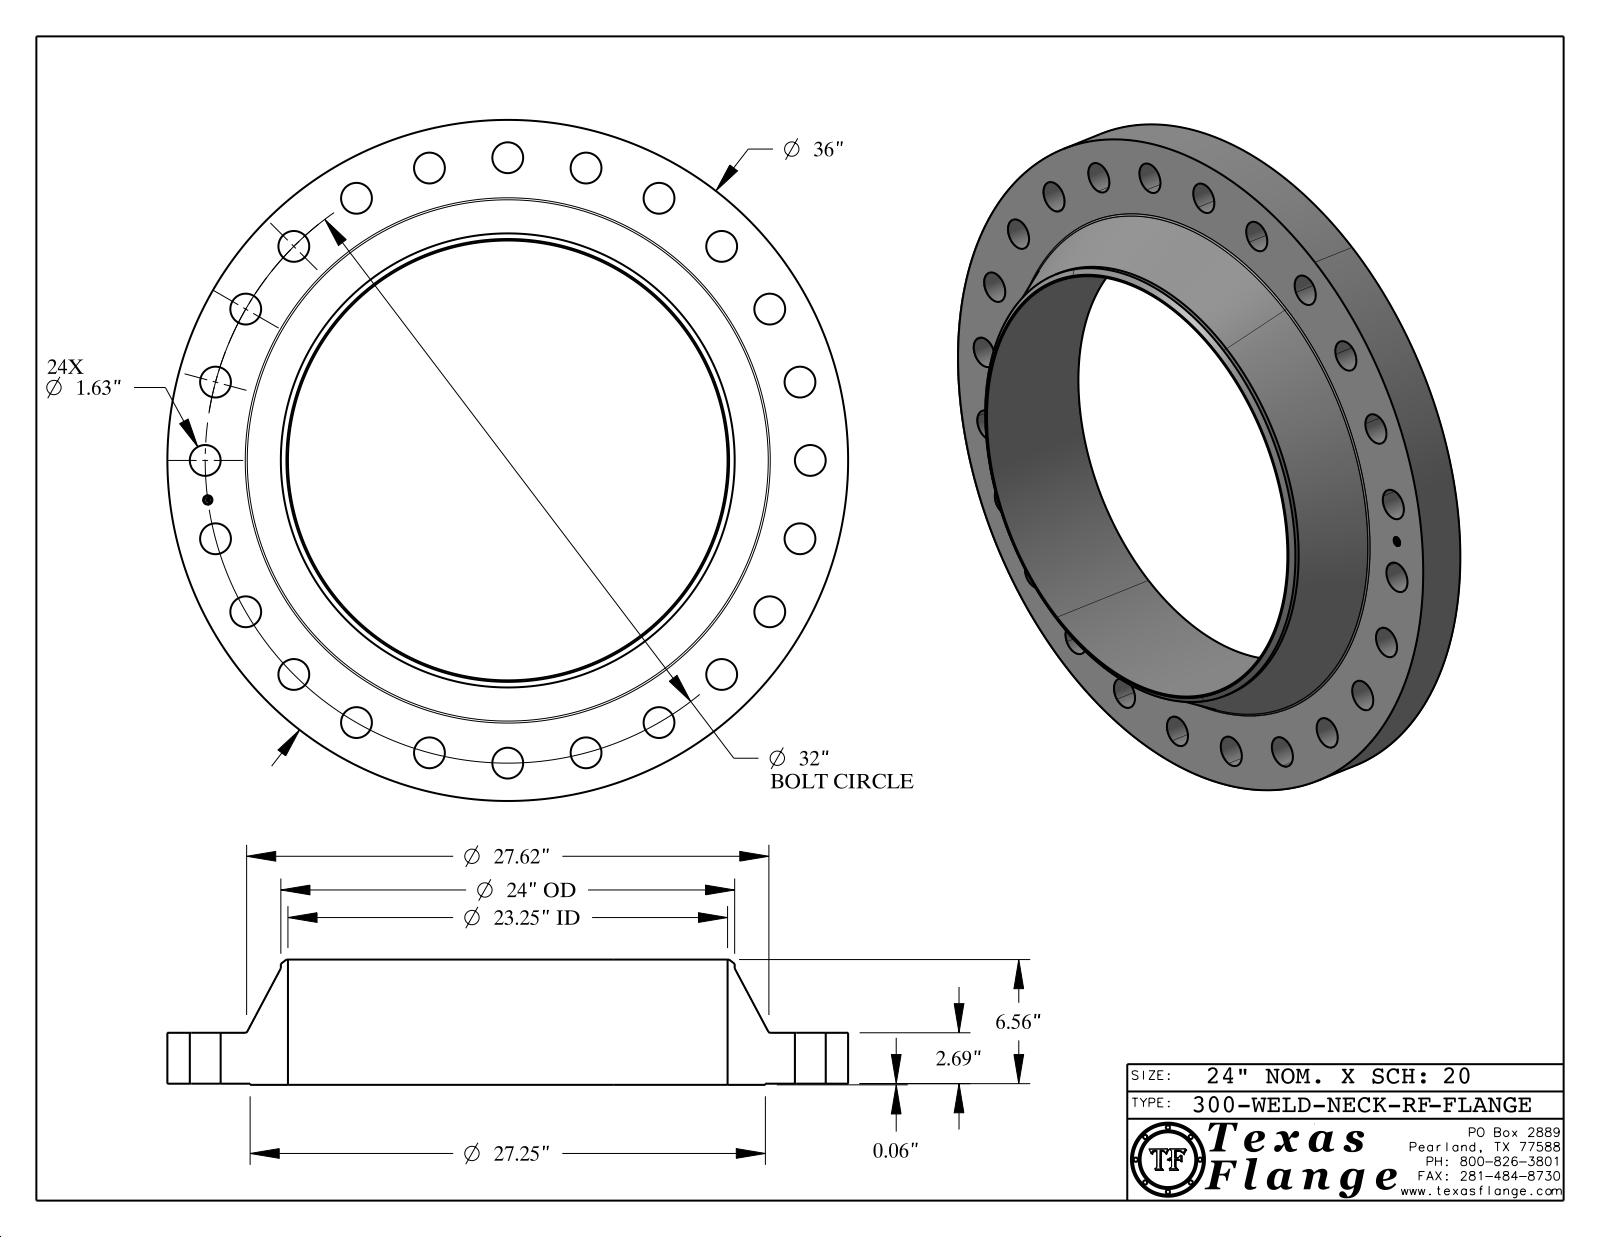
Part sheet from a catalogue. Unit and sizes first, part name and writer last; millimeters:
Units: millimetres
Overall size (bounding box): 914.4 × 914.4 × 168.2
Round holes (diameter × count): ⌀41.4 ×24, ⌀12.6 ×1, ⌀590.6 ×1
Round bosses / shafts (diameter × count): ⌀0.8 ×8, ⌀914.4 ×1, ⌀692.2 ×1, ⌀609.6 ×1, ⌀9.9 ×1
Main face-to-face distances: 68.3, 1.6, 69.9, 168.2, 166.6, 98.3, 69.5, 67.9, 0.4, 98.7
Hole centre spacings: 406.4, 785.1, 106.1, 210.4, 311, 494.8, 574.7, 644.8
Volume: 29 840 000 mm³ · Surface area: 1 548 000 mm²
Bodies: 1 solid, 451 faces (369 planar, 76 cylindrical, 6 other)
Part name (STEP PRODUCT): 300-WELD-NECK-RF
STEP written by: CATIA V5 STEP AP214 (AUTOMOTIVE_DESIGN)
